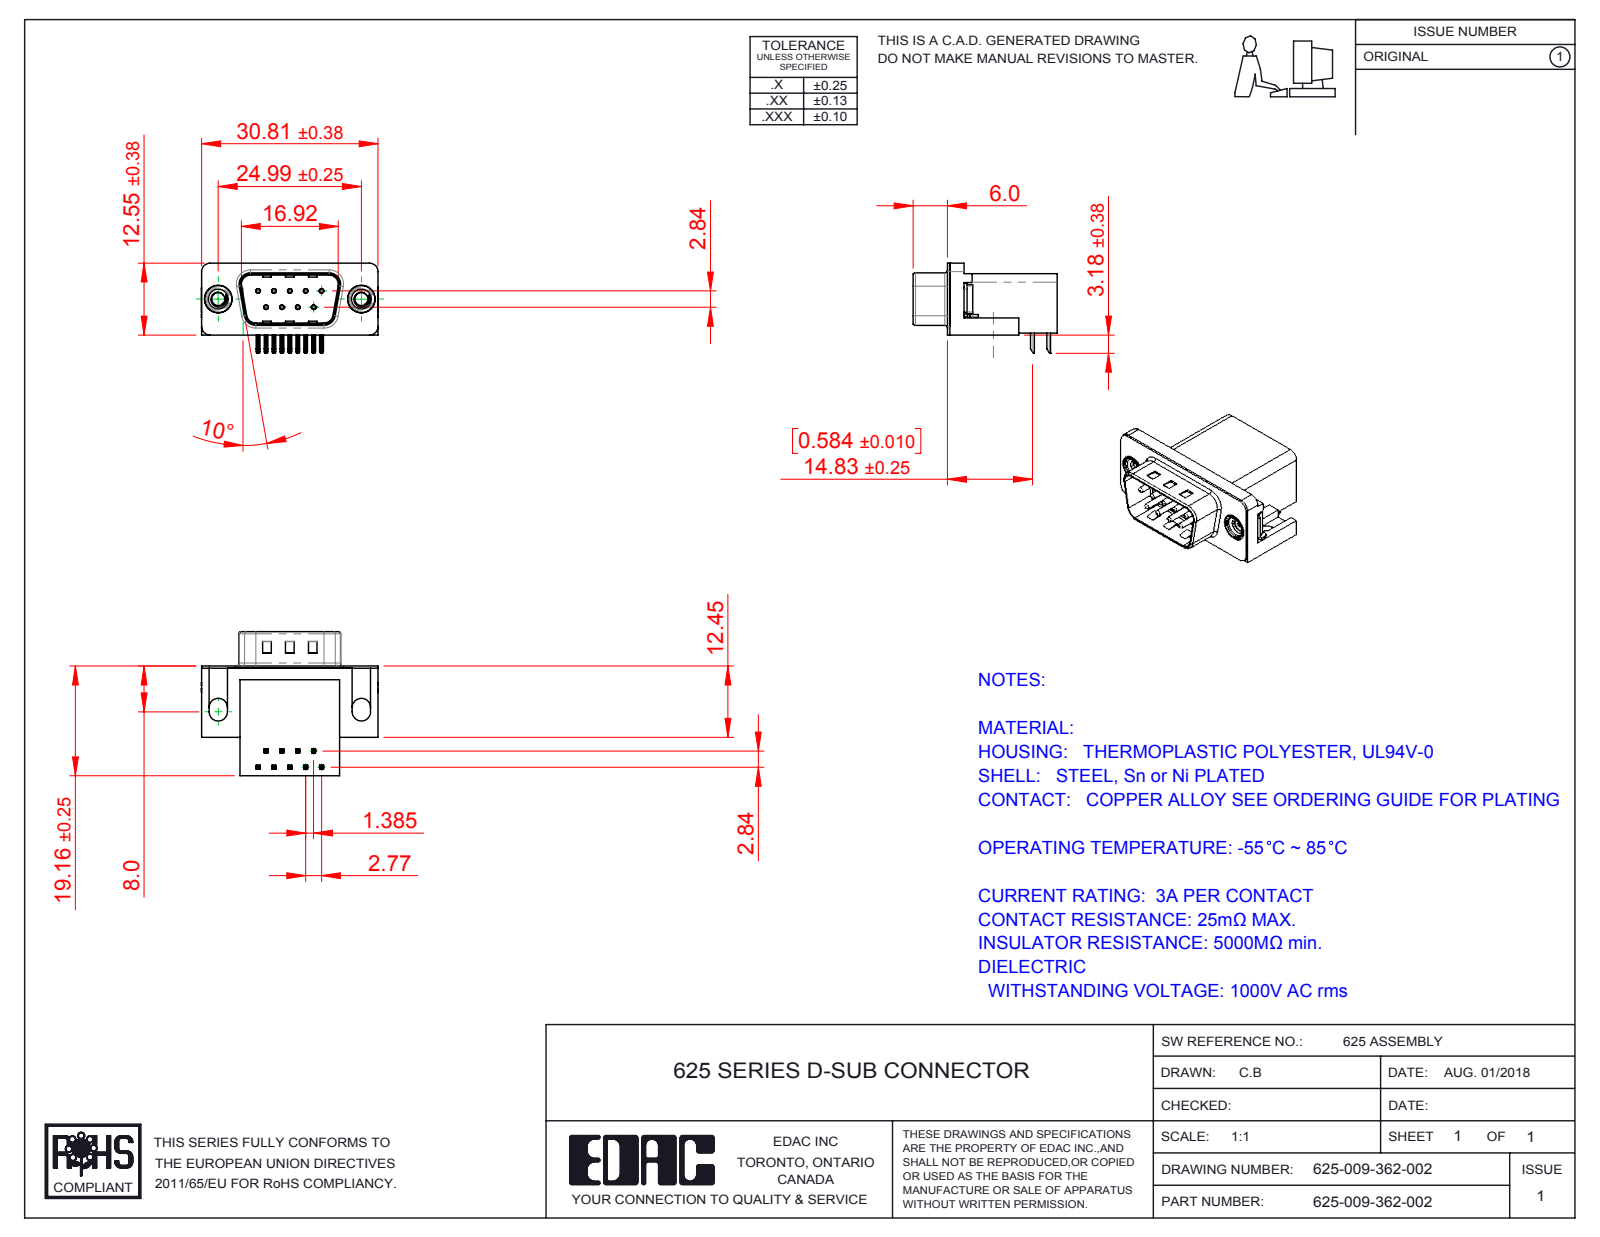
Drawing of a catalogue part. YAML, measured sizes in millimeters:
part_name: "625 4-40 Threaded Rivet; 625 Housing_9 Socket; 625-009-362-002; 625 Contact Top (+3 more)"
step_written_by: "SolidWorks 2016 (CONFIG_CONTROL_DESIGN)"
units: millimeters
bodies: {solids: 15, faces: 991, planar: 575, cylindrical: 313, other: 103}
overall_size: [30.89, 25.16, 15.73]
volume: 4449
surface_area: 4817
round_holes:
  - {diameter: 0.35, count: 9}
  - {diameter: 0.8, count: 9}
  - {diameter: 2.26, count: 2}
  - {diameter: 4, count: 2}
  - {diameter: 4.8, count: 2}
  - {diameter: 5, count: 2}
round_bosses_or_shafts:
  - {diameter: 0.75, count: 9}
  - {diameter: 4.9, count: 2}
  - {diameter: 4.75, count: 2}
  - {diameter: 3.9, count: 2}
partial_cylinders:
  - {radius: 0.25, count: 44}
  - {radius: 0.12, count: 18}
  - {radius: 1, count: 16}
  - {radius: 0.5, count: 9}
  - {radius: 1.5, count: 8}
  - {radius: 1.6, count: 8}
  - {radius: 0.9, count: 4}
  - {radius: 2, count: 4}
face_to_face_distances: [0.4, 10.34, 18.76, 19.16, 2.9, 16.26, 2.5, 0.35, 10.69, 6.7]
hole_center_spacings: [3.16, 2.77, 5.54, 5.03, 5.04, 8.31, 7.48, 7.49]
